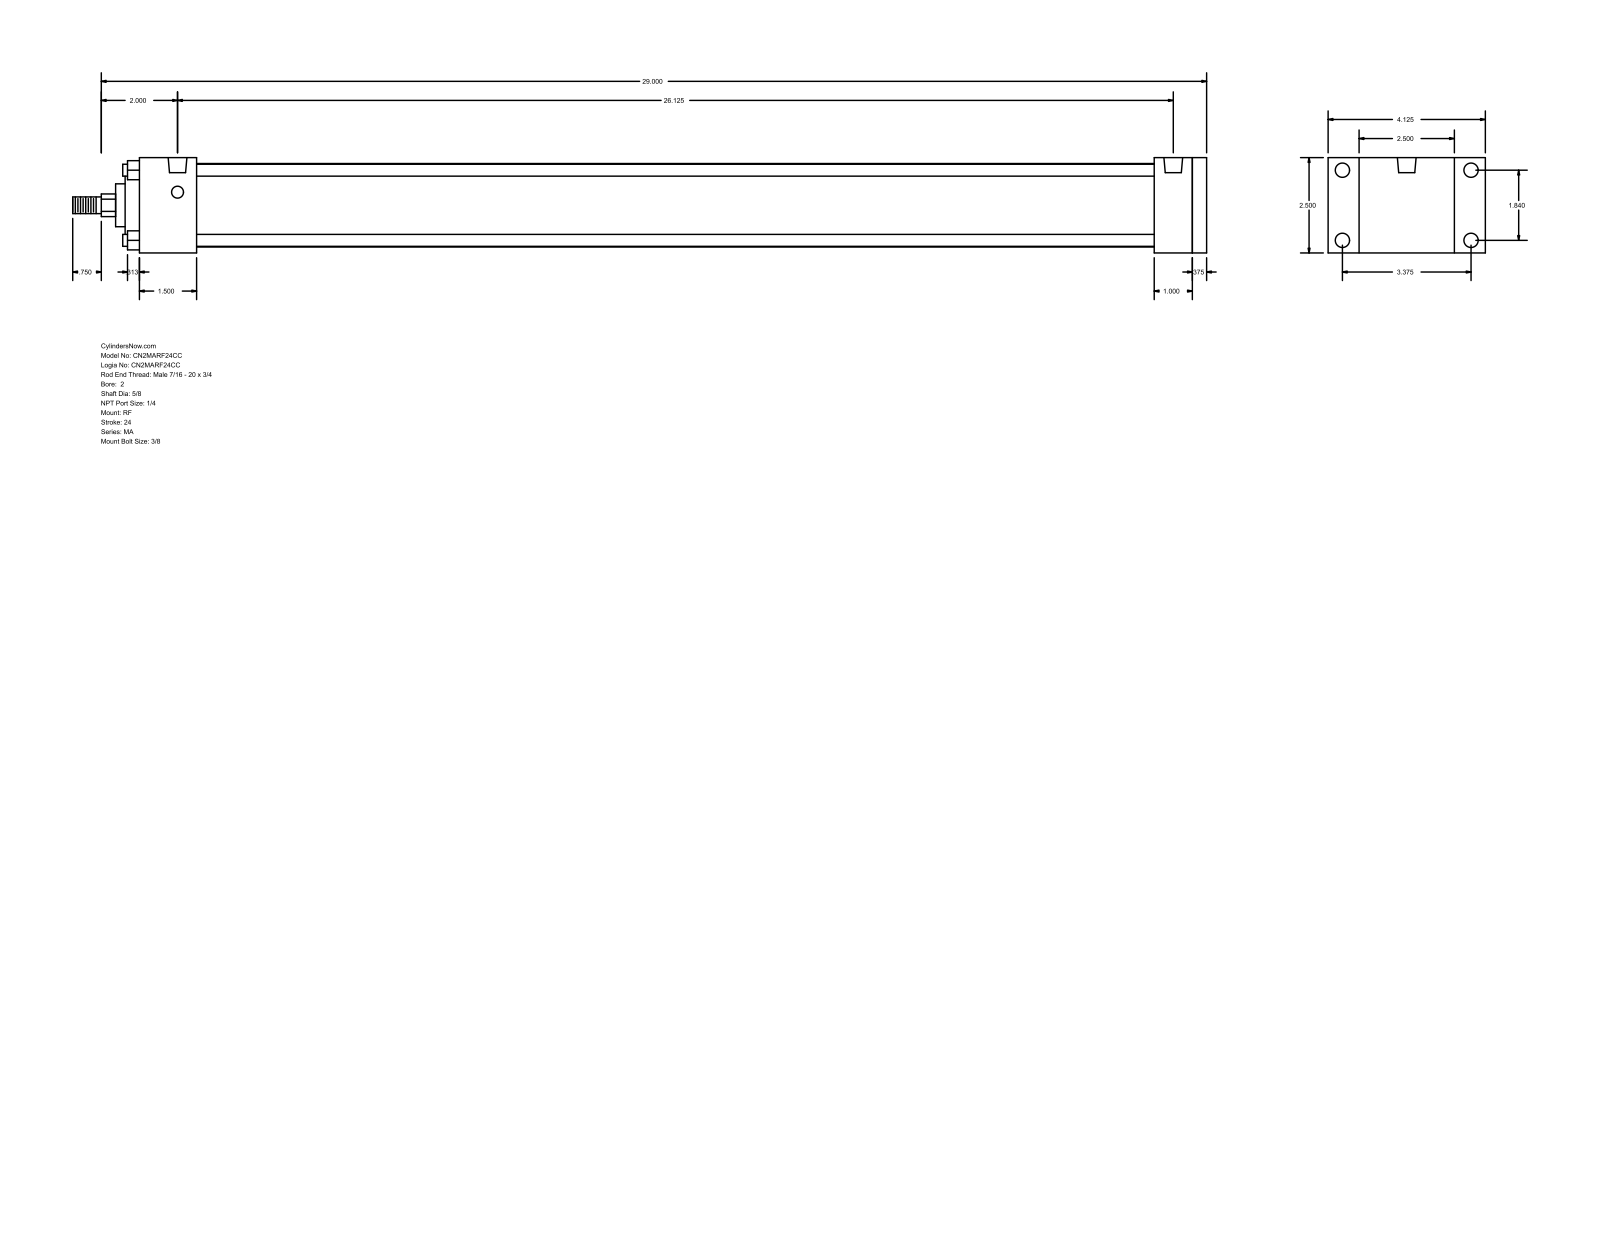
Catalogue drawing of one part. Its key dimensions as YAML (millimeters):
part_name: "MA_RF__0200_0.625"
step_written_by: "GSSL Pune (CONFIG_CONTROL_DESIGN)"
units: millimeters
bodies: {solids: 0, faces: 94, planar: 65, cylindrical: 29, other: 0}
overall_size: [755.65, 104.78, 63.5]
round_holes:
  - {diameter: 7.94, count: 4}
  - {diameter: 9.53, count: 4}
  - {diameter: 12.49, count: 2}
round_bosses_or_shafts:
  - {diameter: 7.94, count: 4}
  - {diameter: 55.63, count: 1}
  - {diameter: 50.8, count: 1}
  - {diameter: 28.57, count: 1}
  - {diameter: 15.88, count: 1}
  - {diameter: 11.11, count: 1}
partial_cylinders:
  - {radius: 7.54, count: 1}
face_to_face_distances: [63.5, 9.52, 711.2, 38.1, 34.93, 720.72, 701.68, 663.58, 673.1, 676.27]
hole_center_spacings: [46.74, 85.72, 97.63, 663.58]
